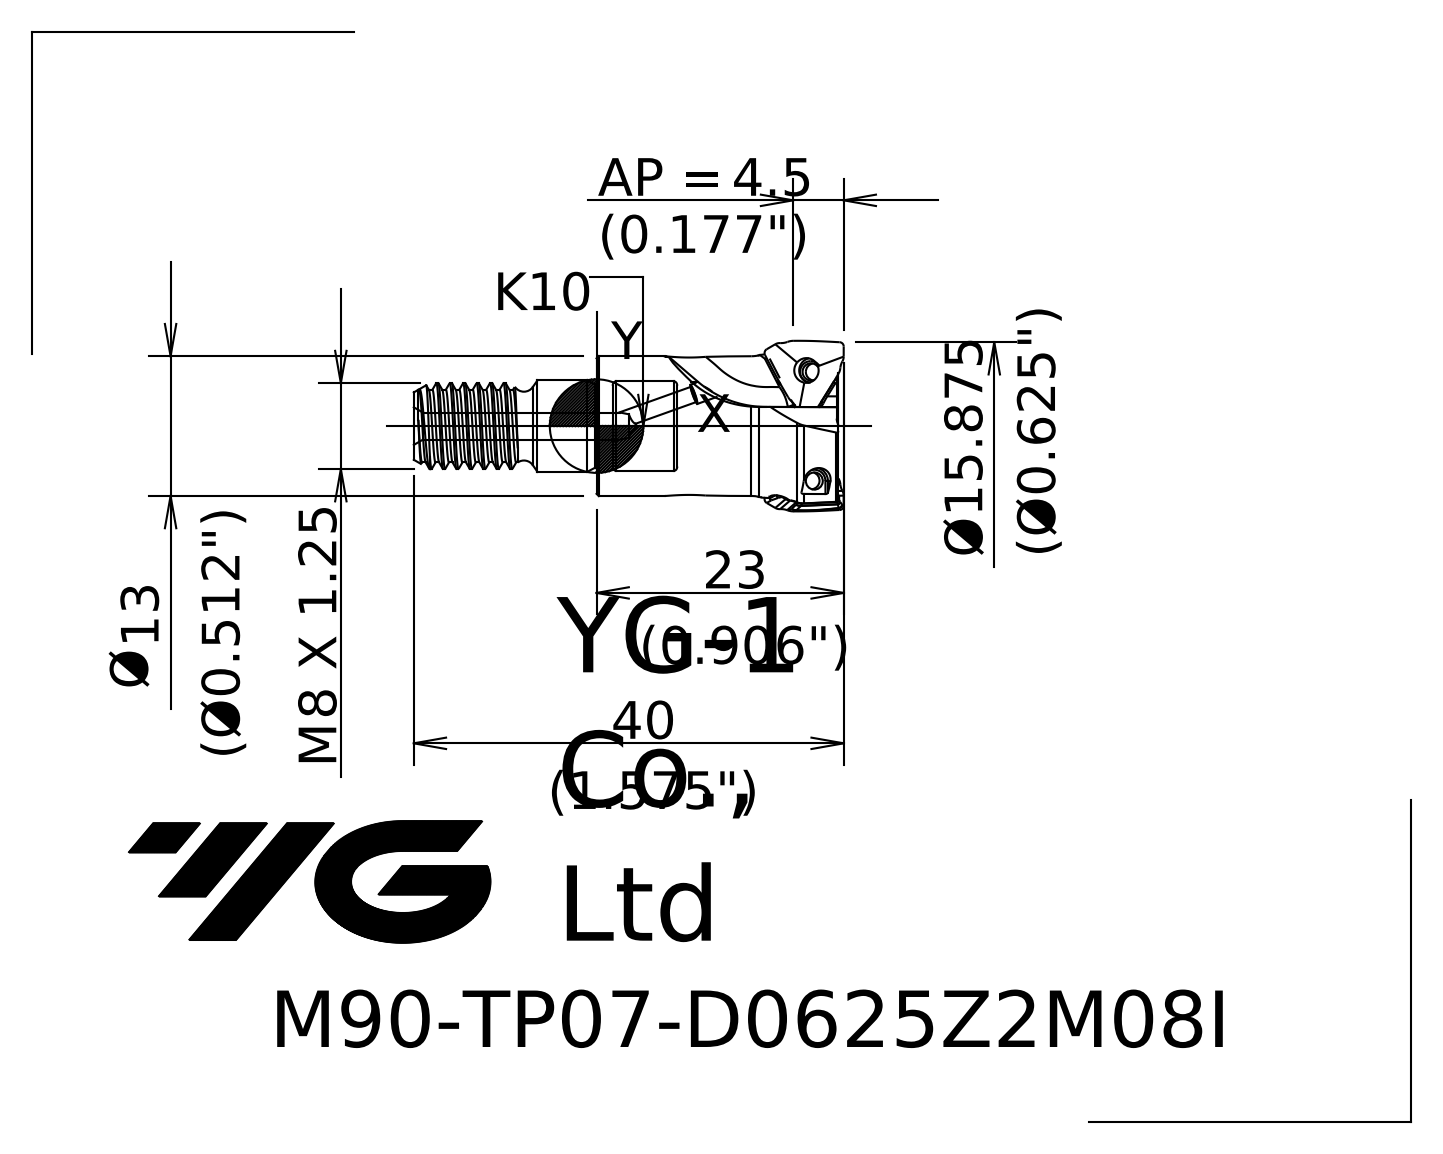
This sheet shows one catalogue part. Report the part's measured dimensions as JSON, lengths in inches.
{"part_name": "102200DC38DB0jr6", "step_written_by": "SIEMENS PLM Software NX 10.0 (AP203_CONFIGURATION_CONTROLLED_3D_DESIGN_OF_MECHANICAL_PARTS_AND_ASSEMBLIES_MIM_LF)", "units": "inches", "bodies": {"solids": 1, "faces": 48, "planar": 9, "cylindrical": 8, "other": 31}, "overall_size": [1.575, 0.626, 0.626], "volume_in3": 0.225, "surface_area_in2": 3.985, "round_holes": [[0.098, 1]], "round_bosses_or_shafts": [[0.512, 1], [0.335, 1], [0.315, 1]], "partial_cylinders_radius": [[0.012, 4]], "face_to_face_distances": [0.394, 0.906, 1.575, 0.669, 0.61, 0.295, 0.965, 0.846, 0.236, 0.059]}
